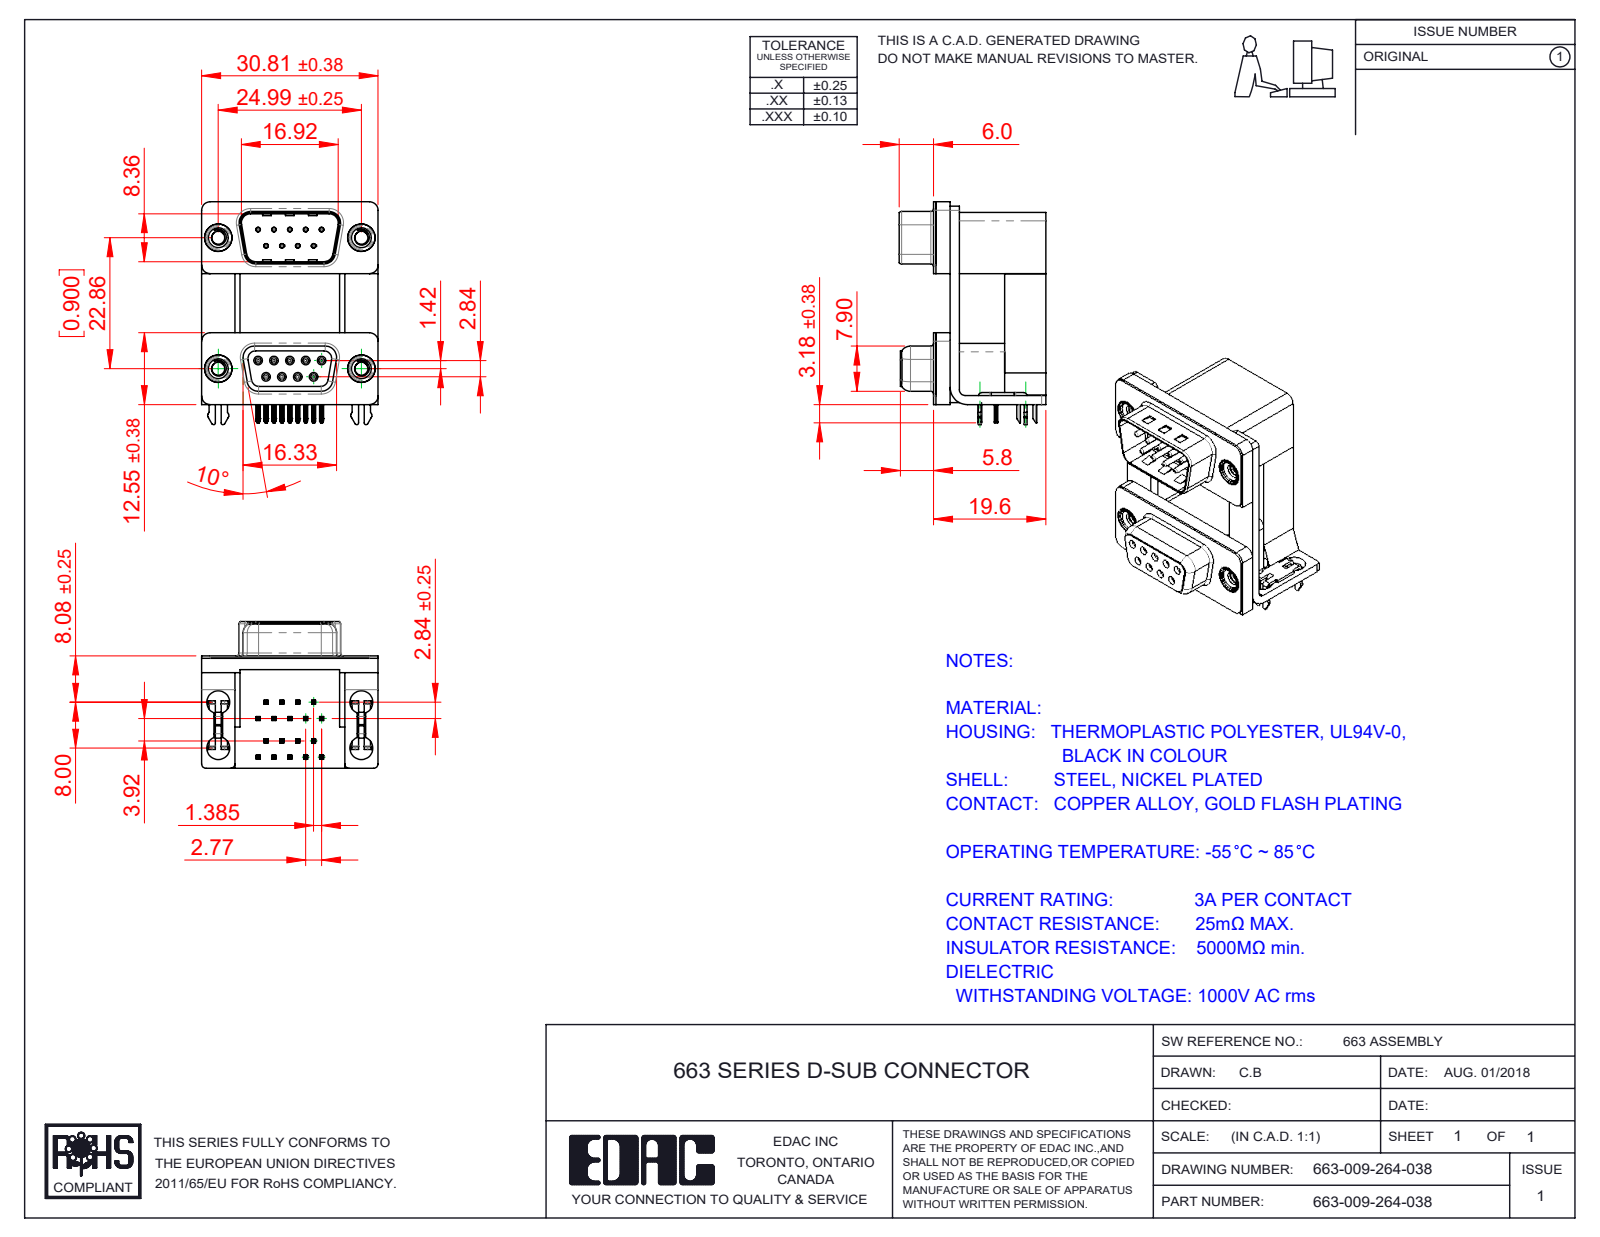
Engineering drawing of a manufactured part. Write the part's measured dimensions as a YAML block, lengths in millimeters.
part_name: "663 2 Prong Board Lock_3; 663-009-264-038; 663 Housing Lower_09 Contacts; 663 Mounting Bracket_2ProngH (+8 more)"
step_written_by: "SolidWorks 2020 (CONFIG_CONTROL_DESIGN)"
units: millimeters
bodies: {solids: 31, faces: 2681, planar: 1365, cylindrical: 745, other: 571}
overall_size: [38.91, 30.81, 25.6]
volume: 11365
surface_area: 13245
round_holes:
  - {diameter: 0.8, count: 18}
  - {diameter: 0.35, count: 9}
  - {diameter: 0.9, count: 9}
  - {diameter: 4, count: 8}
  - {diameter: 2.26, count: 4}
  - {diameter: 3.5, count: 4}
  - {diameter: 4.8, count: 4}
  - {diameter: 5, count: 4}
round_bosses_or_shafts:
  - {diameter: 1.2, count: 9}
  - {diameter: 0.75, count: 9}
  - {diameter: 4.9, count: 4}
  - {diameter: 4.75, count: 4}
  - {diameter: 3.9, count: 4}
partial_cylinders:
  - {radius: 0.1, count: 74}
  - {radius: 0.25, count: 46}
  - {radius: 0.15, count: 36}
  - {radius: 0.12, count: 18}
  - {radius: 0.35, count: 18}
  - {radius: 0.5, count: 16}
  - {radius: 1.5, count: 15}
  - {radius: 0.75, count: 10}
face_to_face_distances: [2.5, 0.4, 19.2, 16.7, 12, 9.5, 7.2, 1.6, 12.4, 19.6]
hole_center_spacings: [3.16, 2.77, 23.03, 22.86, 5.54, 23.52, 20.07, 25.74]
